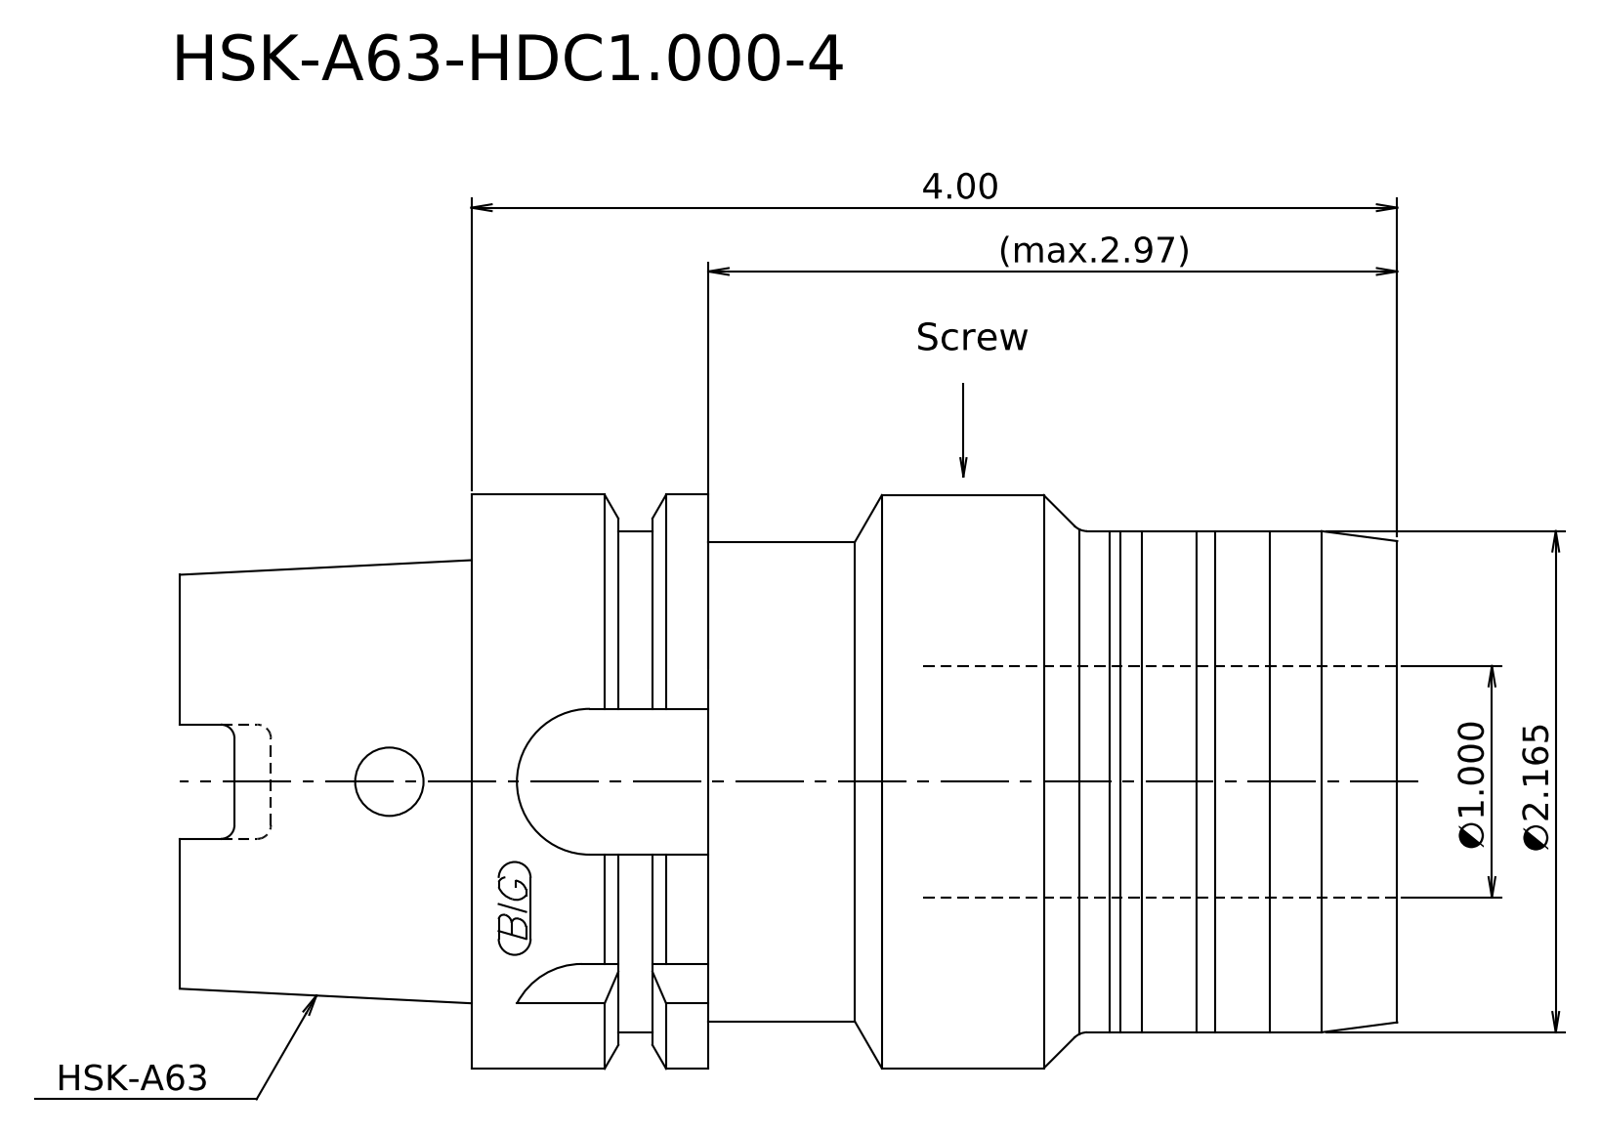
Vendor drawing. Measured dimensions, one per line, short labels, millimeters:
written by: Kubotek KeyCreator 2011 V10.0.2 (22737) (automotive_design)
unit: mm
bodies: 1 solid, 18 faces (6 planar, 6 cylindrical, 6 other)
size: 133.6 × 63 × 63
volume: 324 150 mm³; area: 31 096 mm²
bosses: 1× ⌀63, 1× ⌀62.9, 1× ⌀55, 1× ⌀52.6
face distances: 133.6, 101.6, 32, 75.6, 26, 58, 81.72, 6.12, 19.88, 51.88
